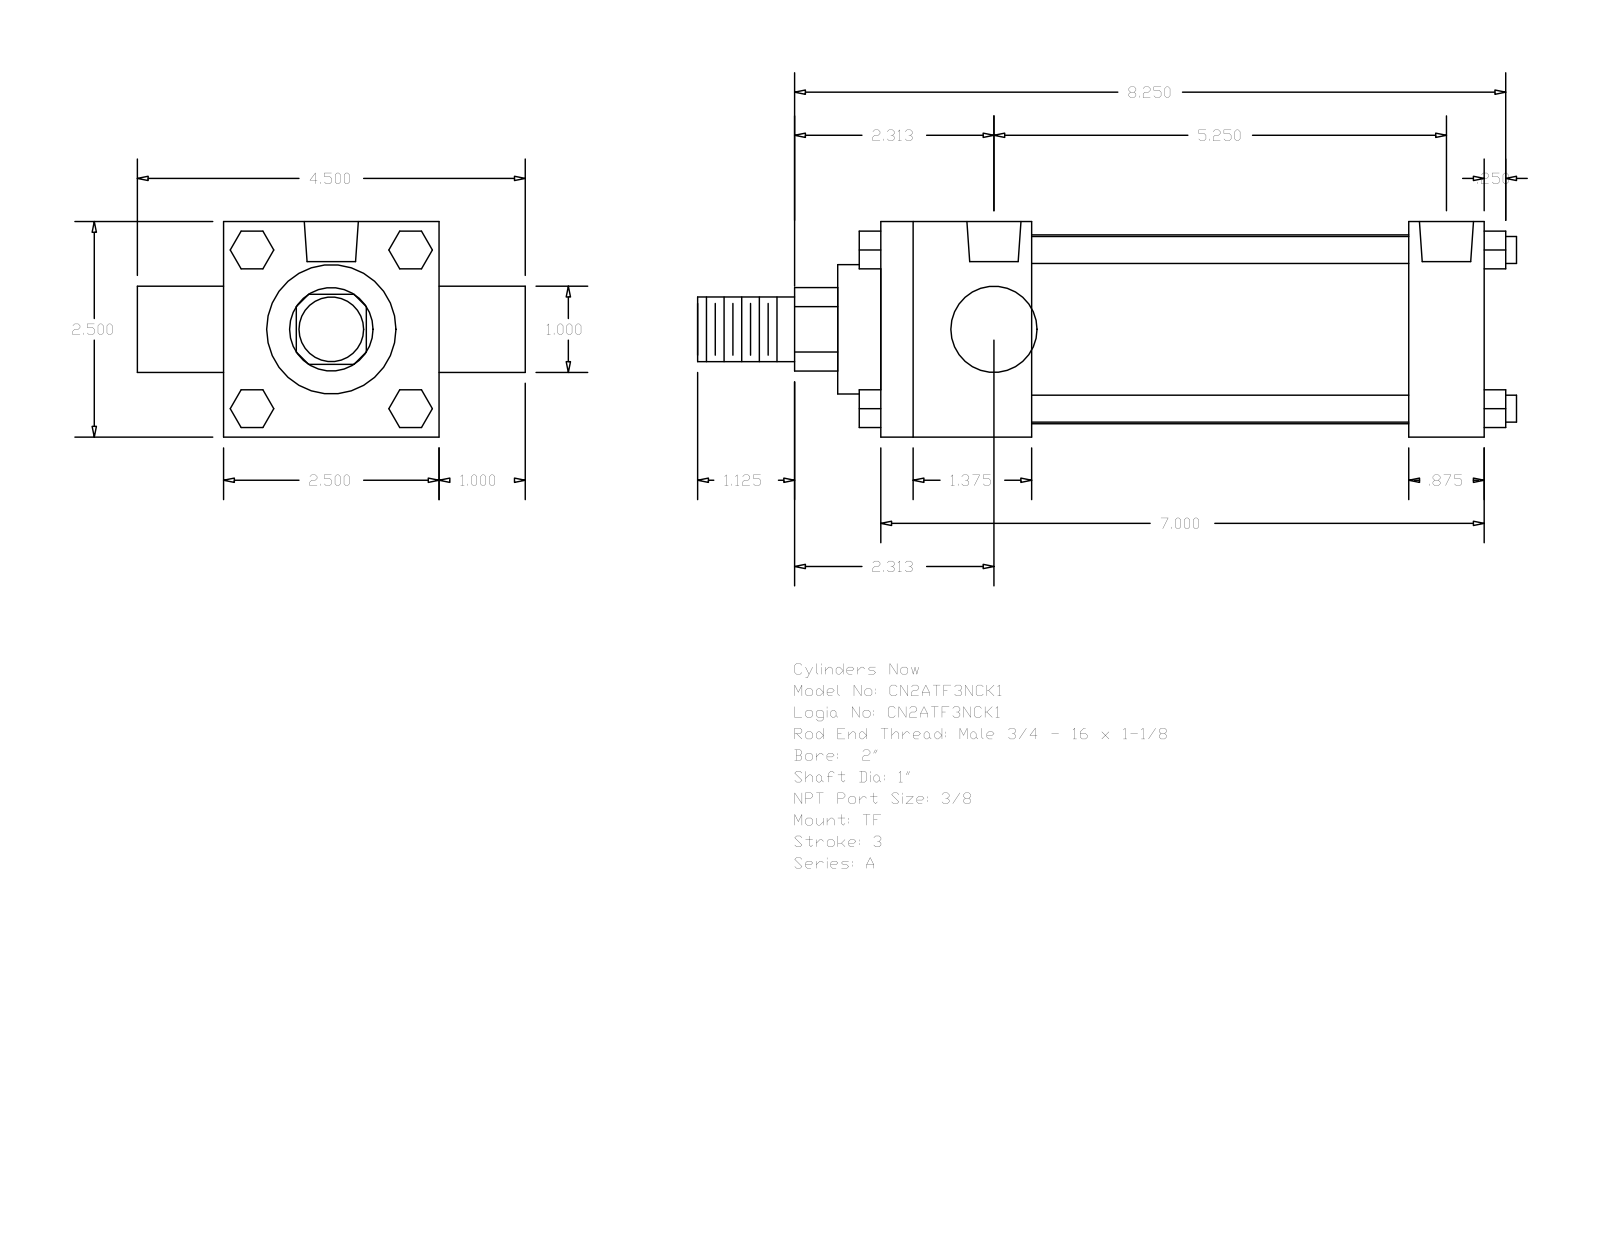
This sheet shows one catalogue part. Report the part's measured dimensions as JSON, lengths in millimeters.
{"part_name": "A_TF__0200_1", "step_written_by": "GSSL Pune (CONFIG_CONTROL_DESIGN)", "units": "millimeters", "bodies": {"solids": 0, "faces": 120, "planar": 92, "cylindrical": 28, "other": 0}, "overall_size": [241.3, 114.3, 63.5], "round_holes": [[5.56, 3], [15.93, 2]], "round_bosses_or_shafts": [[7.94, 4], [25.4, 2], [55.63, 1], [38.1, 1], [19.05, 1]], "partial_cylinders_radius": [[12.29, 1]], "face_to_face_distances": [63.5, 177.8, 44.45, 155.57, 111.12, 133.35, 22.23, 25.4, 88.9, 190.5], "hole_center_spacings": [1.59, 3.98, 127.78, 129.37, 131.76, 133.35]}
